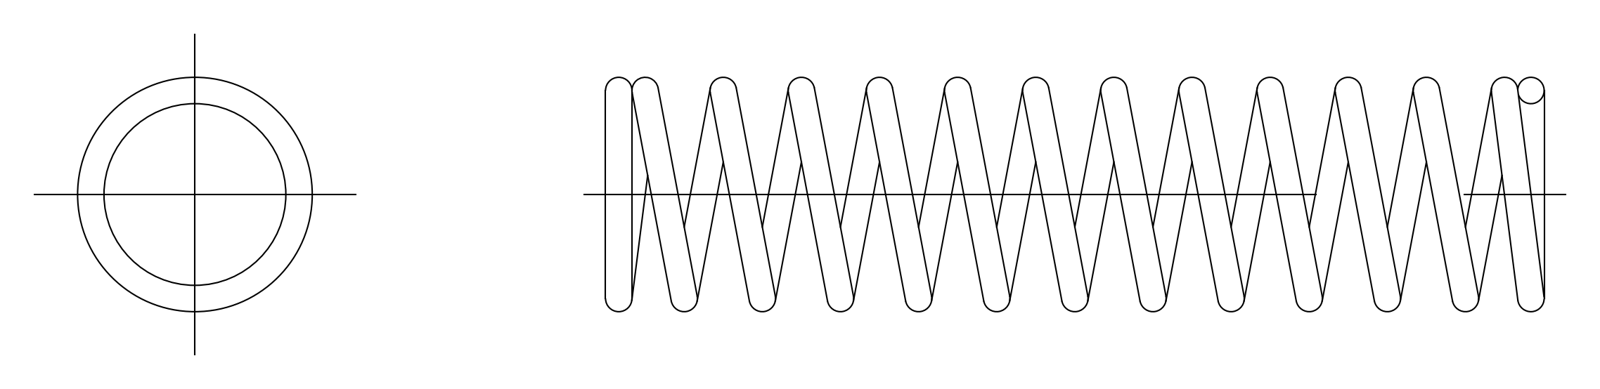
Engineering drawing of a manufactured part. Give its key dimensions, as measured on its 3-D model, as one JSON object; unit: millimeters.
{"part_name": "PC002-prt0; PC002-prt1; PC002-prt2; PC002-prt3 (+7 more)", "step_written_by": "spGate 19.8.4 (****-****-****-****) (AUTOMOTIVE_DESIGN)", "units": "millimeters", "bodies": {"solids": 1, "faces": 102, "planar": 2, "cylindrical": 0, "other": 100}, "overall_size": [32, 8, 8], "volume_mm3": 183, "surface_area_mm2": 821}
